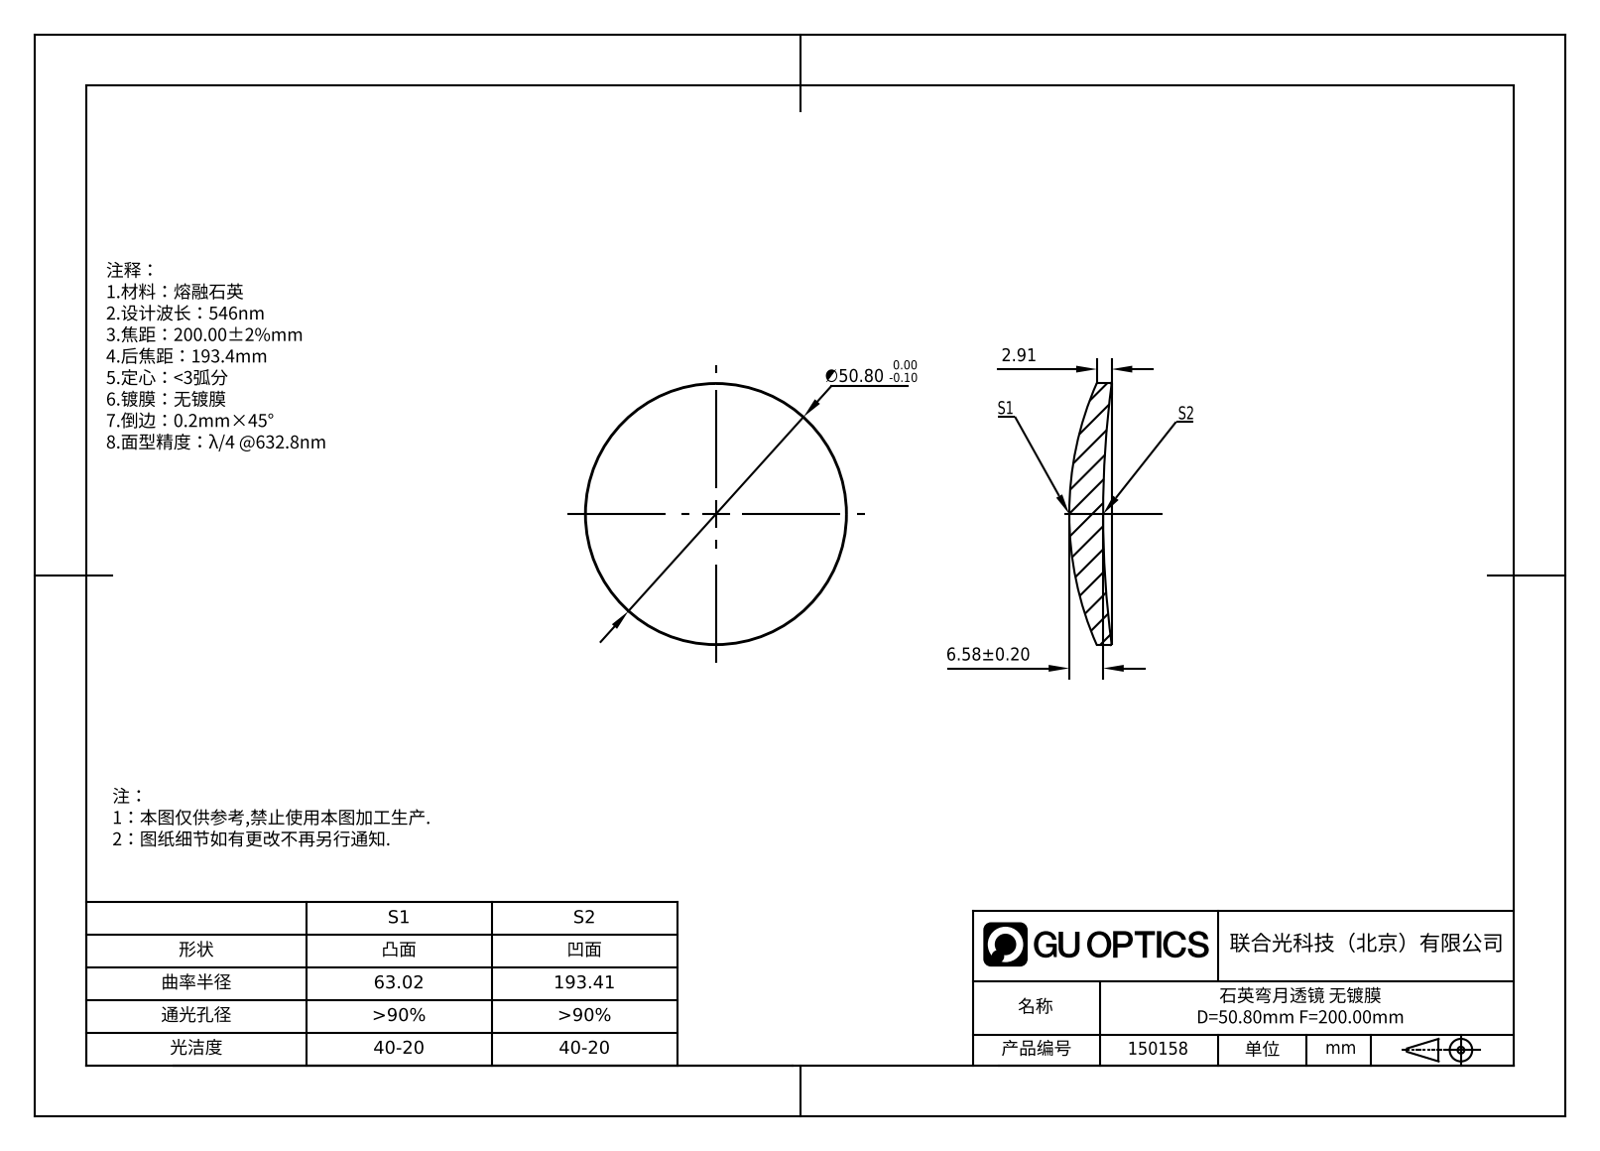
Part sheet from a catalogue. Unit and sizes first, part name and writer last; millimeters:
Units: millimetres
Overall size (bounding box): 50.8 × 50.8 × 8.22
Round bosses / shafts (diameter × count): ⌀50.8 ×1
Volume: 9 672 mm³ · Surface area: 4 595 mm²
Bodies: 1 solid, 8 faces (0 planar, 2 cylindrical, 6 other)
Part name (STEP PRODUCT): GLM2-050B-200
STEP written by: SolidWorks 2022 (AUTOMOTIVE_DESIGN)
